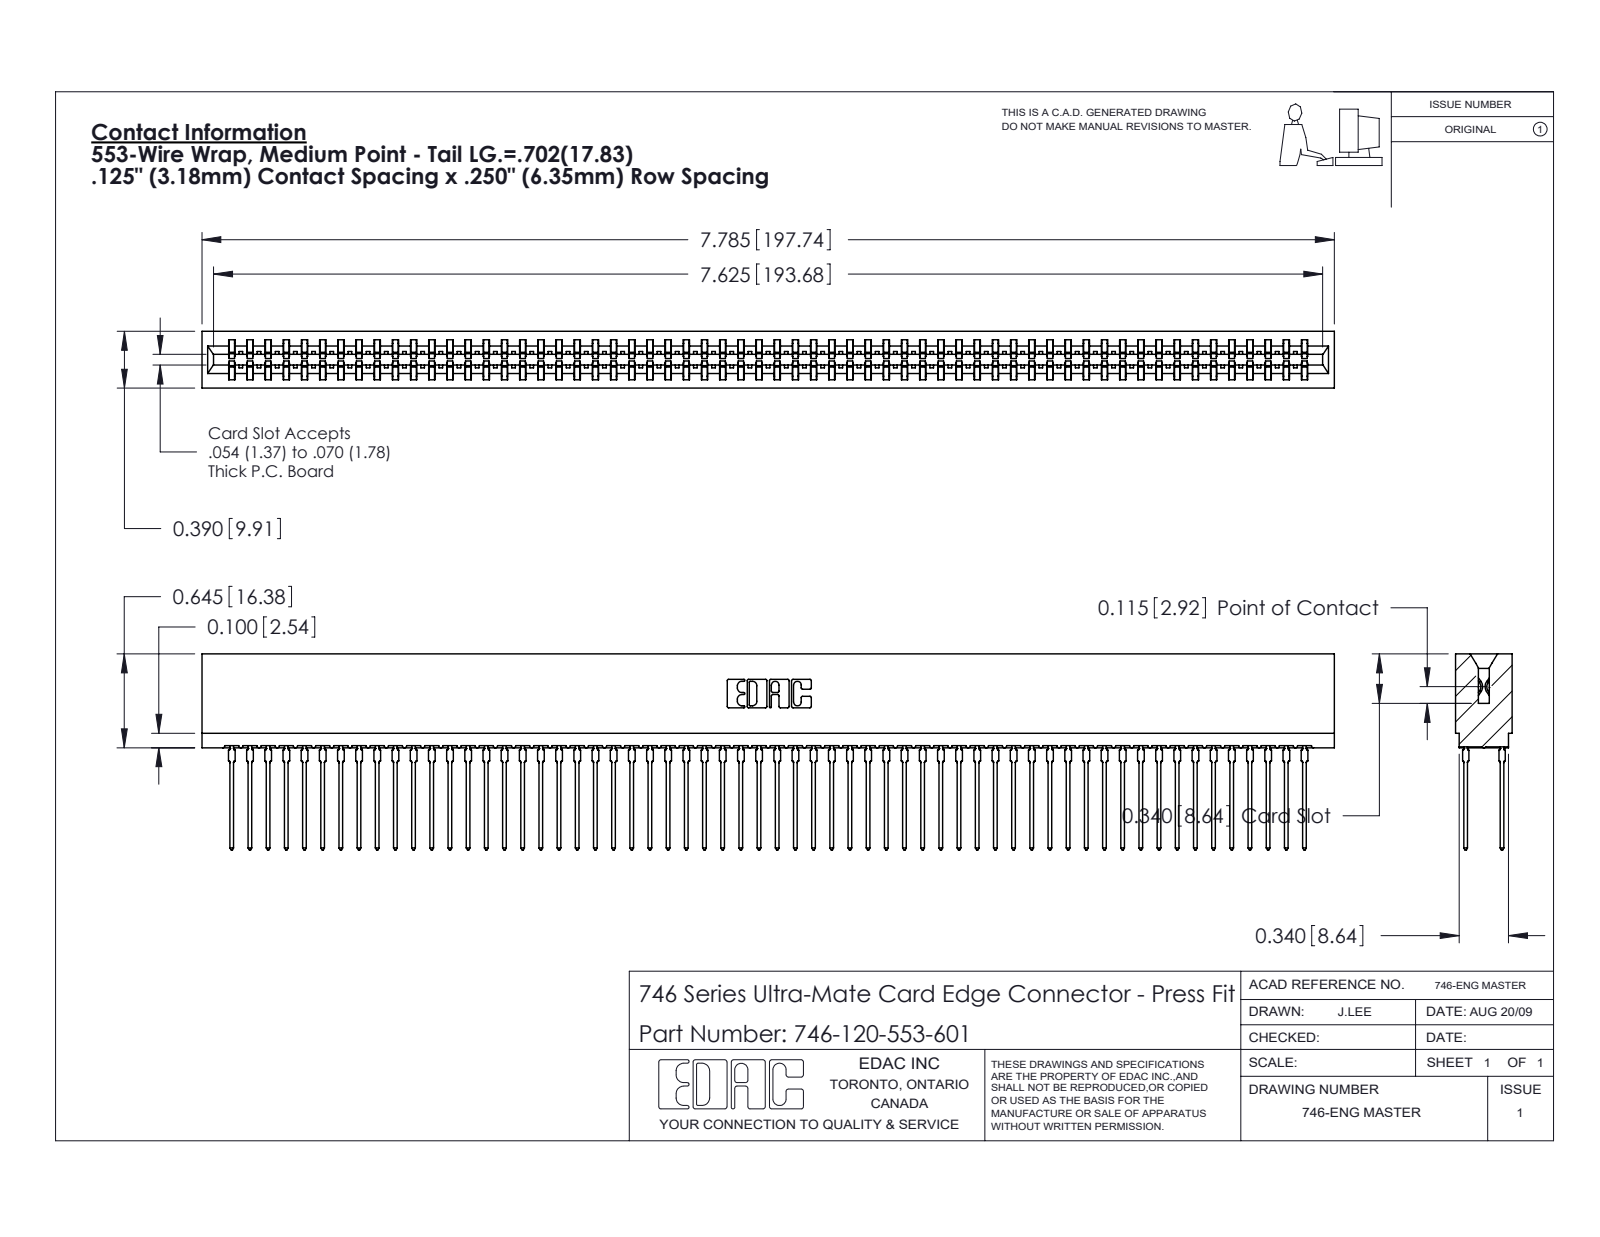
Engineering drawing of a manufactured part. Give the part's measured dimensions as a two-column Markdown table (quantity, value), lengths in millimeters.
| quantity | value |
| --- | --- |
| part name | 746 Part_.340 Slot Depth - 01; 746-292-001_553; 746-120-553-601 |
| STEP written by | SolidWorks 2020 (CONFIG_CONTROL_DESIGN) |
| units | millimeters |
| bodies | 121 solids, 10837 faces (5575 planar, 2142 cylindrical, 3120 other) |
| overall size | 197.7 × 34.2 × 9.9 |
| volume | 23 170 mm³ |
| surface area | 36 810 mm² |
| partial cylindrical surfaces (radius × count) | 0.5 × 240, 0.4 × 61, 0.3 × 22, 0.1 × 8, 0.3 × 8, 0.2 × 6, 0.8 × 6, 0.7 × 3 |
| main face-to-face distances | 1.4, 8.5, 0.6, 6.4, 7.8, 9.9, 2.1, 7, 5.7, 0.4 |
